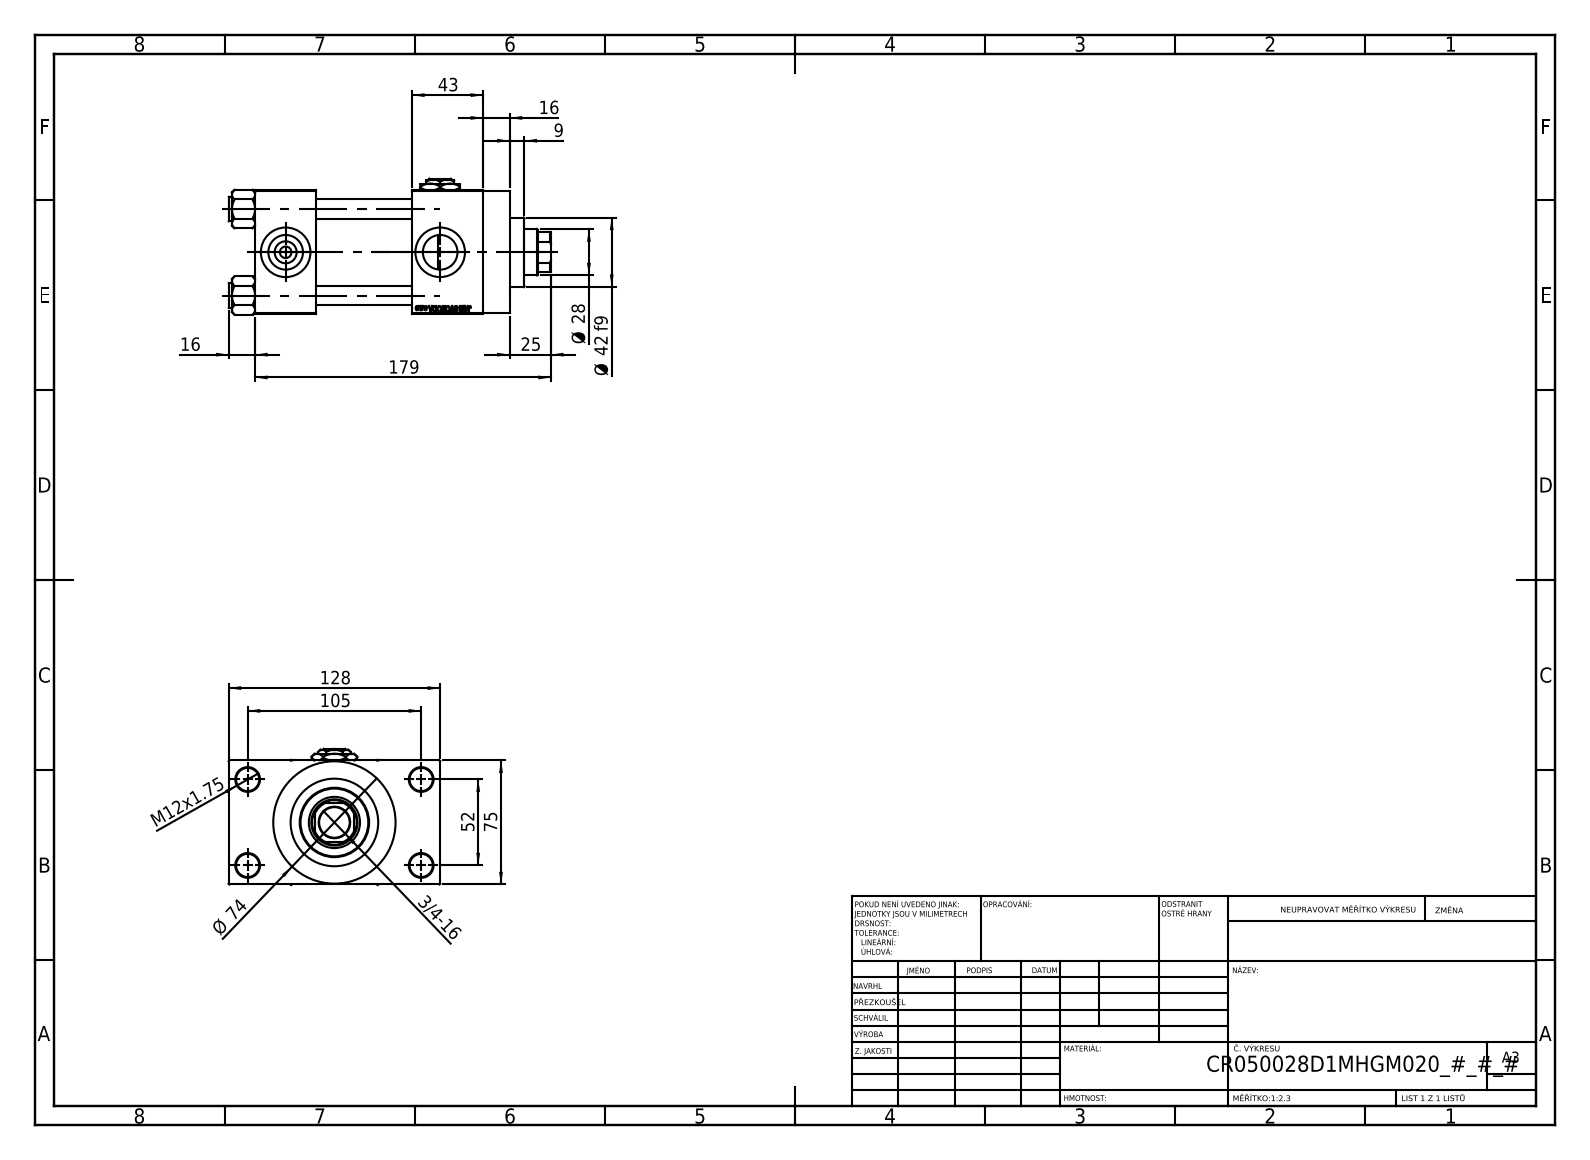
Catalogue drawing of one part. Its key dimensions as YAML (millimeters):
part_name: "V215CR_D_TYCINKA; Zatka_pro_OIL_PORT; NUT_M5_D; V215_VC_A (+2 more)"
step_written_by: "SolidWorks 2019 (CONFIG_CONTROL_DESIGN)"
units: millimeters
bodies: {solids: 12, faces: 1151, planar: 521, cylindrical: 92, other: 538}
overall_size: [195, 128, 82.27]
volume: 803995
surface_area: 172236
round_holes:
  - {diameter: 12, count: 4}
  - {diameter: 14, count: 4}
  - {diameter: 20.96, count: 3}
  - {diameter: 30, count: 3}
  - {diameter: 7, count: 2}
  - {diameter: 18.5, count: 1}
  - {diameter: 28, count: 1}
  - {diameter: 31, count: 1}
  - {diameter: 41, count: 1}
  - {diameter: 50, count: 1}
  - {diameter: 53, count: 1}
round_bosses_or_shafts:
  - {diameter: 15, count: 4}
  - {diameter: 74, count: 1}
  - {diameter: 56, count: 1}
  - {diameter: 42, count: 1}
partial_cylinders:
  - {radius: 13.5, count: 1}
face_to_face_distances: [75, 58, 37, 95, 26.5, 138, 101, 43, 101.5, 16]
hole_center_spacings: [26.35, 36.98, 52.3, 58.43, 58.59, 78.65, 94.37, 52]
